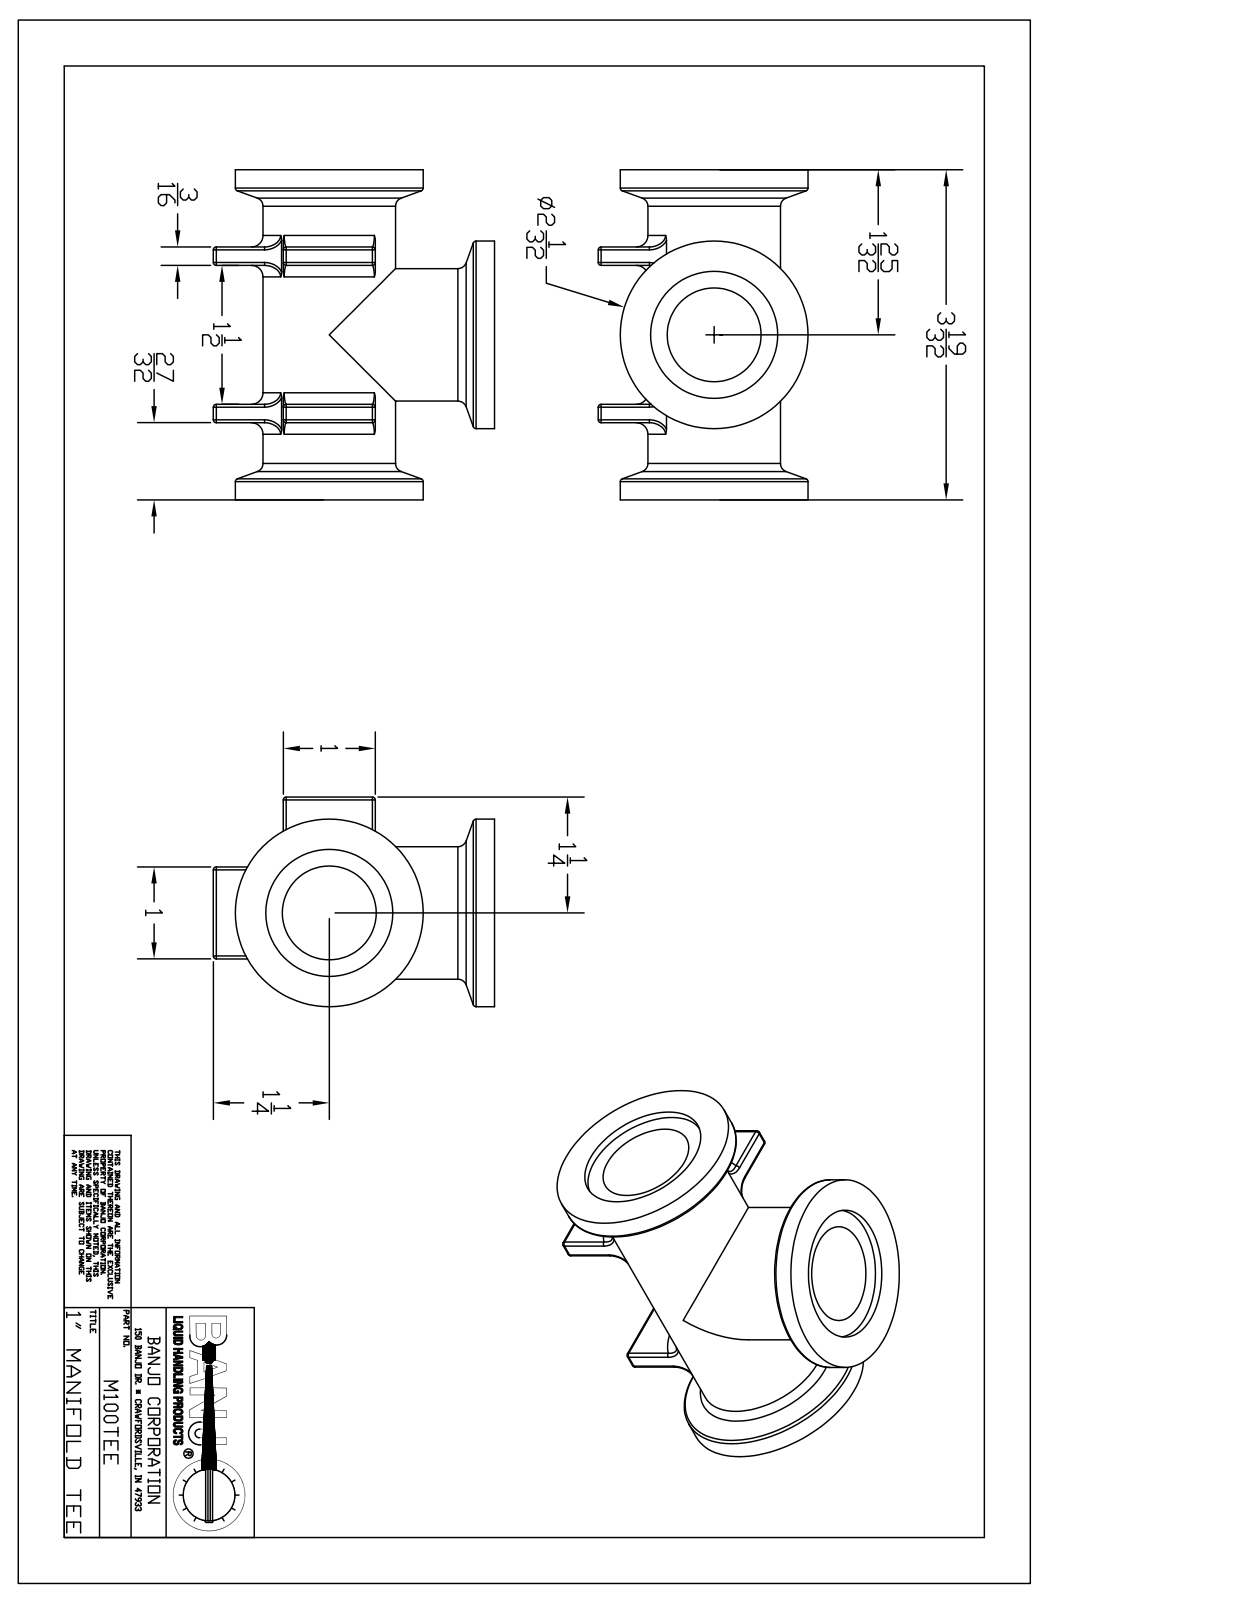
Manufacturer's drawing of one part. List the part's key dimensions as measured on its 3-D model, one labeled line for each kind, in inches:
Part name (STEP PRODUCT): M100TEE
STEP written by: Autodesk Inventor 2012 (AUTOMOTIVE_DESIGN)
Units: inches
Bodies: 1 solid, 461 faces (178 planar, 81 cylindrical, 202 other)
Overall size (bounding box): 3.59 × 3.055 × 2.28
Volume: 5.424 in³ · Surface area: 52.79 in²
Round holes (diameter × count): ⌀1.02 ×2, ⌀1.38 ×2
Round bosses / shafts (diameter × count): ⌀2.04 ×2, ⌀1.44 ×2
Partial cylindrical surfaces — rounded edges, fillets, slot ends (radius × count): R0.03 ×24, R0.125 ×4, R0.06 ×3, R0.74 ×1
Main face-to-face distances: 0.084, 0.84, 1.04, 2.55, 2.75, 1.71, 0.2, 3.59, 3.506, 0.756
